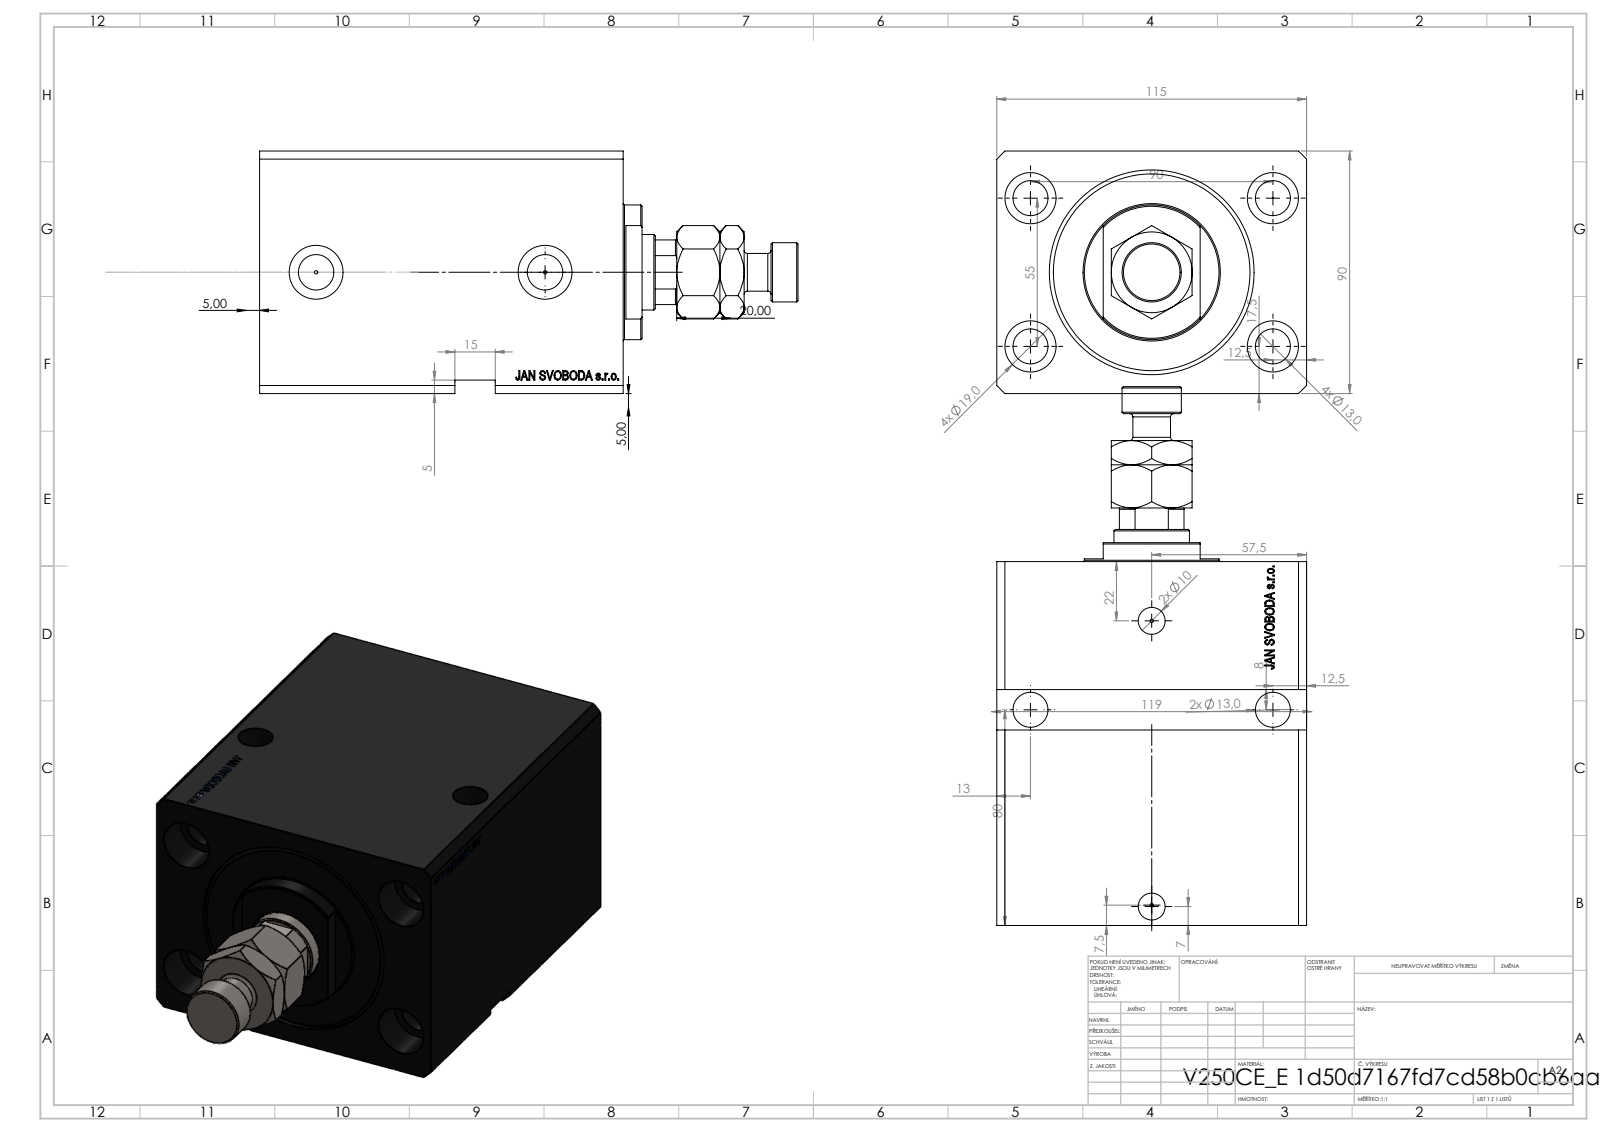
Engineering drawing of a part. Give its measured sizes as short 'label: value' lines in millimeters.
name: V250CE_VC_E; V250CE_C_VCP; V250CE_E_Body; MFA
written by: SolidWorks 2019 (CONFIG_CONTROL_DESIGN)
unit: mm
bodies: 4 solids, 1009 faces (483 planar, 108 cylindrical, 418 other)
size: 200 × 115 × 90
volume: 1 169 000 mm³; area: 179 473 mm²
holes: 8× ⌀13, 4× ⌀1.25, 4× ⌀19, 2× ⌀10, 2× ⌀13.16, 2× ⌀20, 1× ⌀18.5, 1× ⌀28, 1× ⌀63, 1× ⌀76
bosses: 1× ⌀50, 1× ⌀22, 1× ⌀14
rounds: 1× R13.5
face distances: 115, 90, 20, 135, 17.9, 117.1, 97.1, 65, 47.1, 50
hole spacings: 52.74, 55.8, 85.76, 90, 40, 55, 55.49, 85.3
